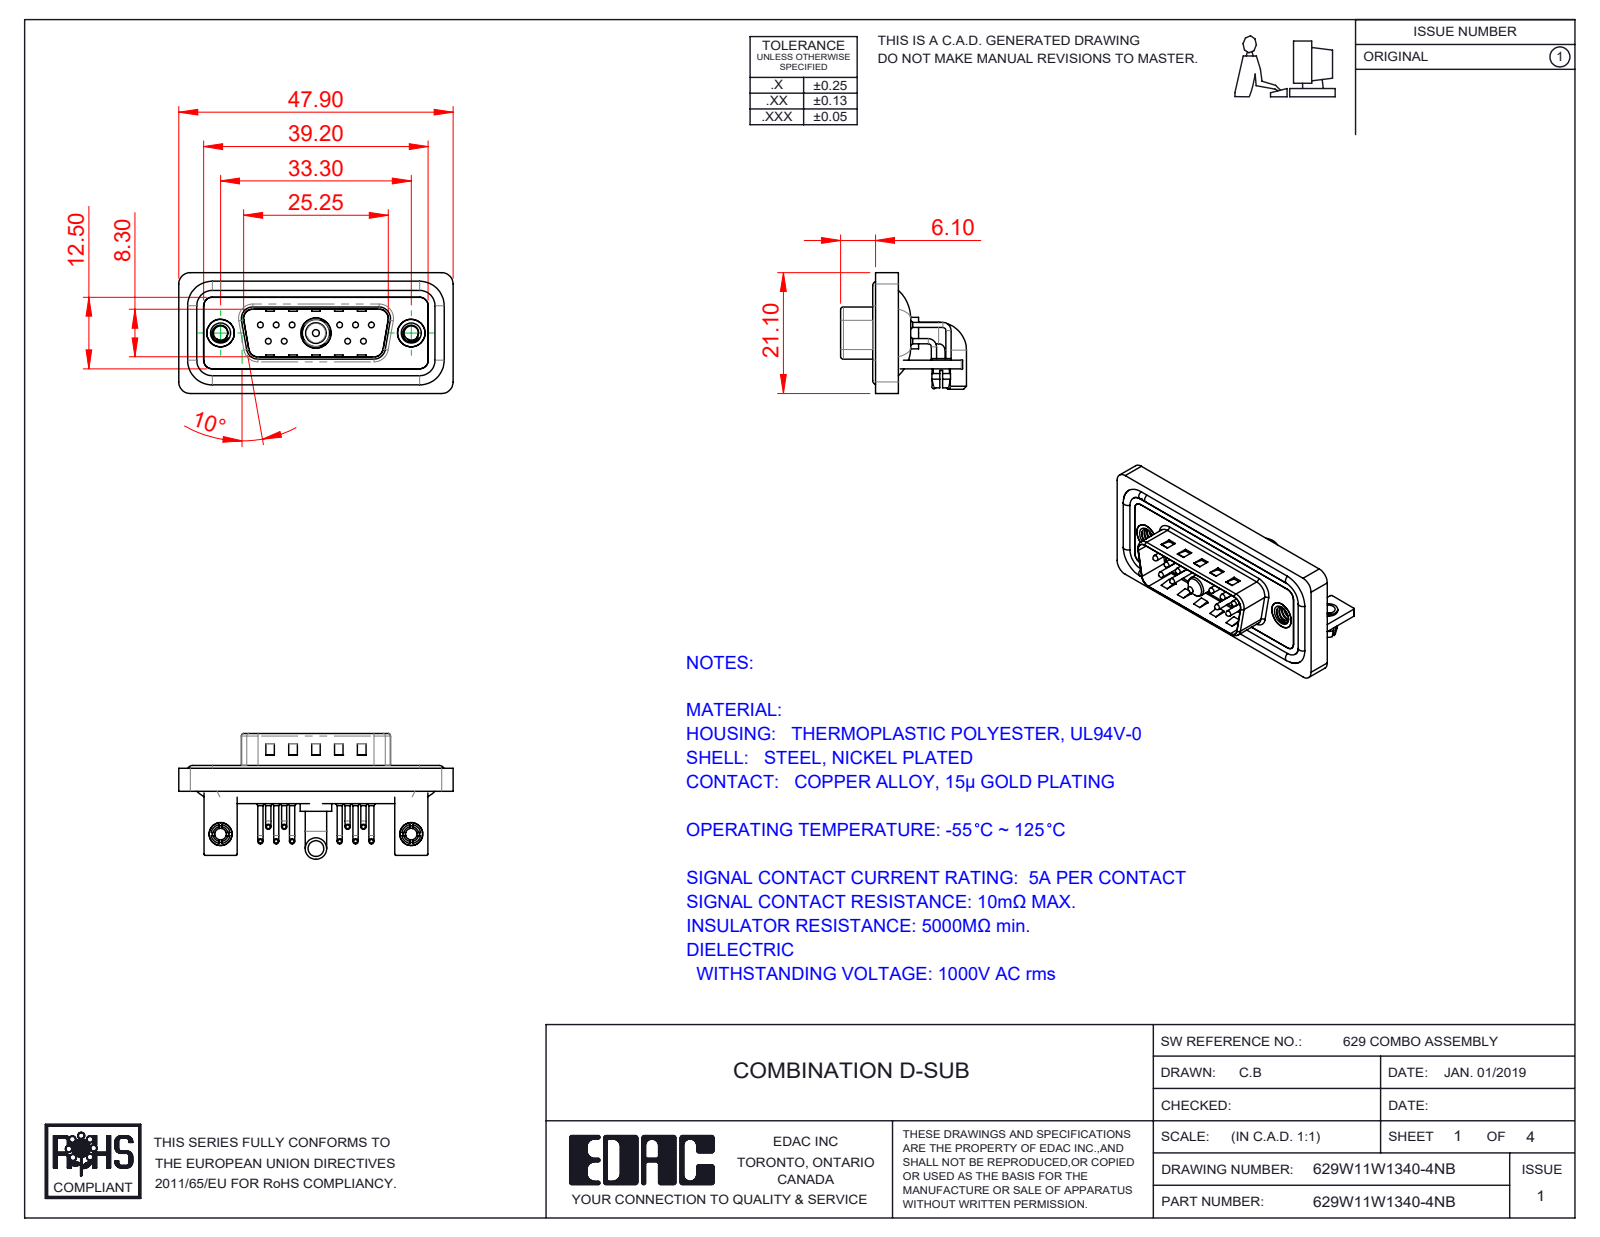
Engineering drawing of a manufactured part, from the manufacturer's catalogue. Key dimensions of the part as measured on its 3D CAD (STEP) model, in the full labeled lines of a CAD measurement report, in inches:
Part name (STEP PRODUCT): 629Combo Board Lock; 629Combo Waterproof Housing_15 Contacts; 629Combo Contact Row 1; 629Combo Stabilizer Bracket (+7 more)
STEP written by: SolidWorks 2023 (CONFIG_CONTROL_DESIGN)
Units: inches
Bodies: 23 solids, 1733 faces (904 planar, 619 cylindrical, 210 other)
Overall size (bounding box): 1.886 × 0.865 × 0.831
Volume: 0.364 in³ · Surface area: 15.69 in²
Round holes (diameter × count): ⌀0.079 ×12, ⌀0.03 ×10, ⌀0.063 ×10, ⌀0.098 ×4, ⌀0.126 ×2, ⌀0.157 ×2, ⌀0.189 ×2, ⌀0.197 ×2, ⌀0.191 ×1, ⌀0.209 ×1
Round bosses / shafts (diameter × count): ⌀0.035 ×20, ⌀0.059 ×10, ⌀0.039 ×10, ⌀0.026 ×10, ⌀0.063 ×4, ⌀0.193 ×2, ⌀0.157 ×2, ⌀0.148 ×2
Partial cylindrical surfaces — rounded edges, fillets, slot ends (radius × count): R0.079 ×21, R0.059 ×18, R0.01 ×16, R0.04 ×10, R0.02 ×9, R0.063 ×8, R0.039 ×7, R0.024 ×4
Main face-to-face distances: 0.016, 0.031, 0.059, 0.114, 0.083, 0.043, 0.063, 0.047, 0.146, 0.161
Hole centre spacings: 0.124, 0.109, 0.545, 0.436, 0.654, 0.198, 0.198, 0.218
